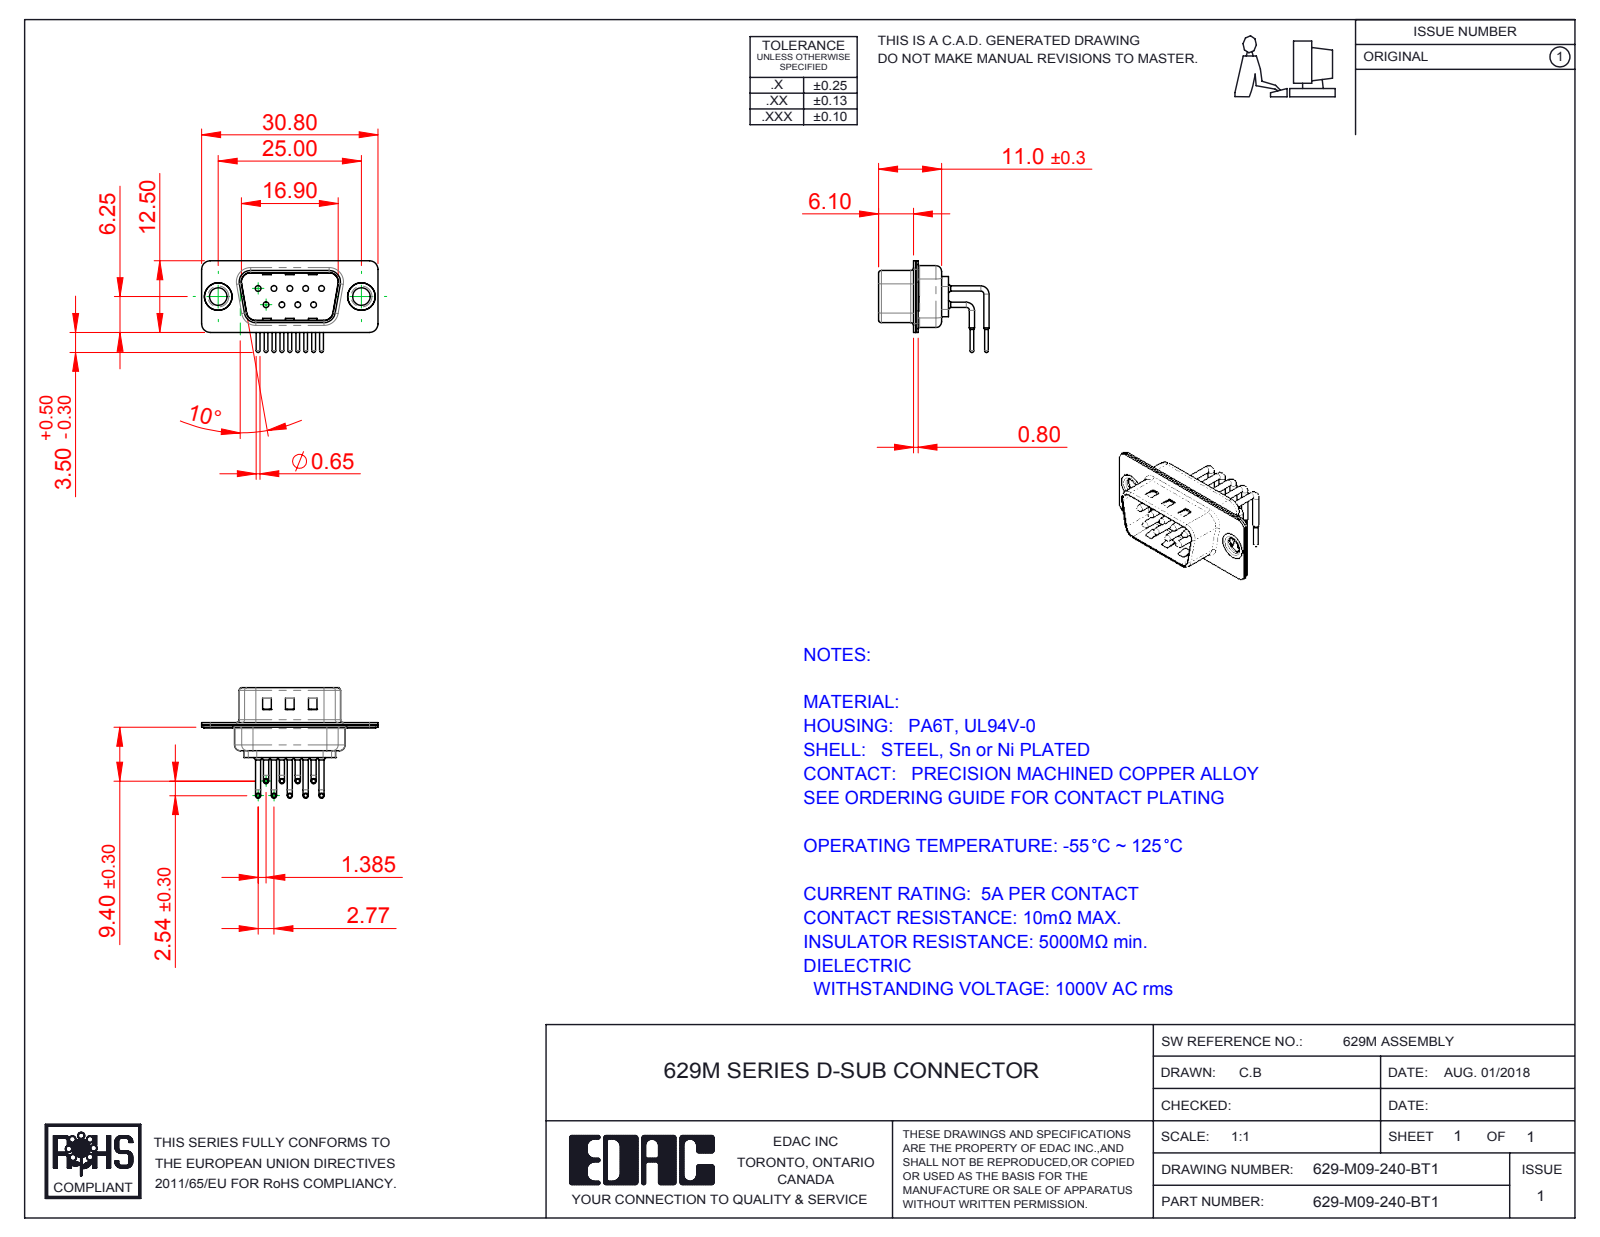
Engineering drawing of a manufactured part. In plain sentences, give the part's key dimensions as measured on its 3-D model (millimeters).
The part is named "629-M09-240-BT1; 629M Thru Hole Rivet; 629M Contact Row 2; 629M Shell Front_09 Contacts (+3 more)". Its 3-D file was written by "SolidWorks 2016 (CONFIG_CONTROL_DESIGN)". It is 14 solids with 1268 faces: 683 planar, 437 cylindrical and 148 other. Overall it measures 30.8 by 19.29 by 16 millimeters. Its volume is 1 302 cubic millimeters and its surface area 3 762 square millimeters. Round holes: 9 of diameter 1, 9 of diameter 1.7, 9 of diameter 2, 2 of diameter 3.05, 2 of diameter 4, 2 of diameter 4.8. Round bosses or shafts: 18 of diameter 0.9, 9 of diameter 1.5, 9 of diameter 0.65, 2 of diameter 5, 2 of diameter 4.9, 2 of diameter 3.55. Partial cylindrical surfaces (rounded edges, fillets, slot ends): 16 of radius 1.5, 12 of radius 2, 9 of radius 1.01, 8 of radius 0.5, 8 of radius 1.6, 4 of radius 0.25, 4 of radius 0.6, 4 of radius 0.65. The main face-to-face distances are 0.4, 0.85, 0.8, 9.55, 1.25, 10.4, 8.7, 0.35, 6.1, 5.7. The hole center spacings are 3.16, 2.77, 5.54, 5.03, 5.04, 8.31, 7.1, 7.48.
